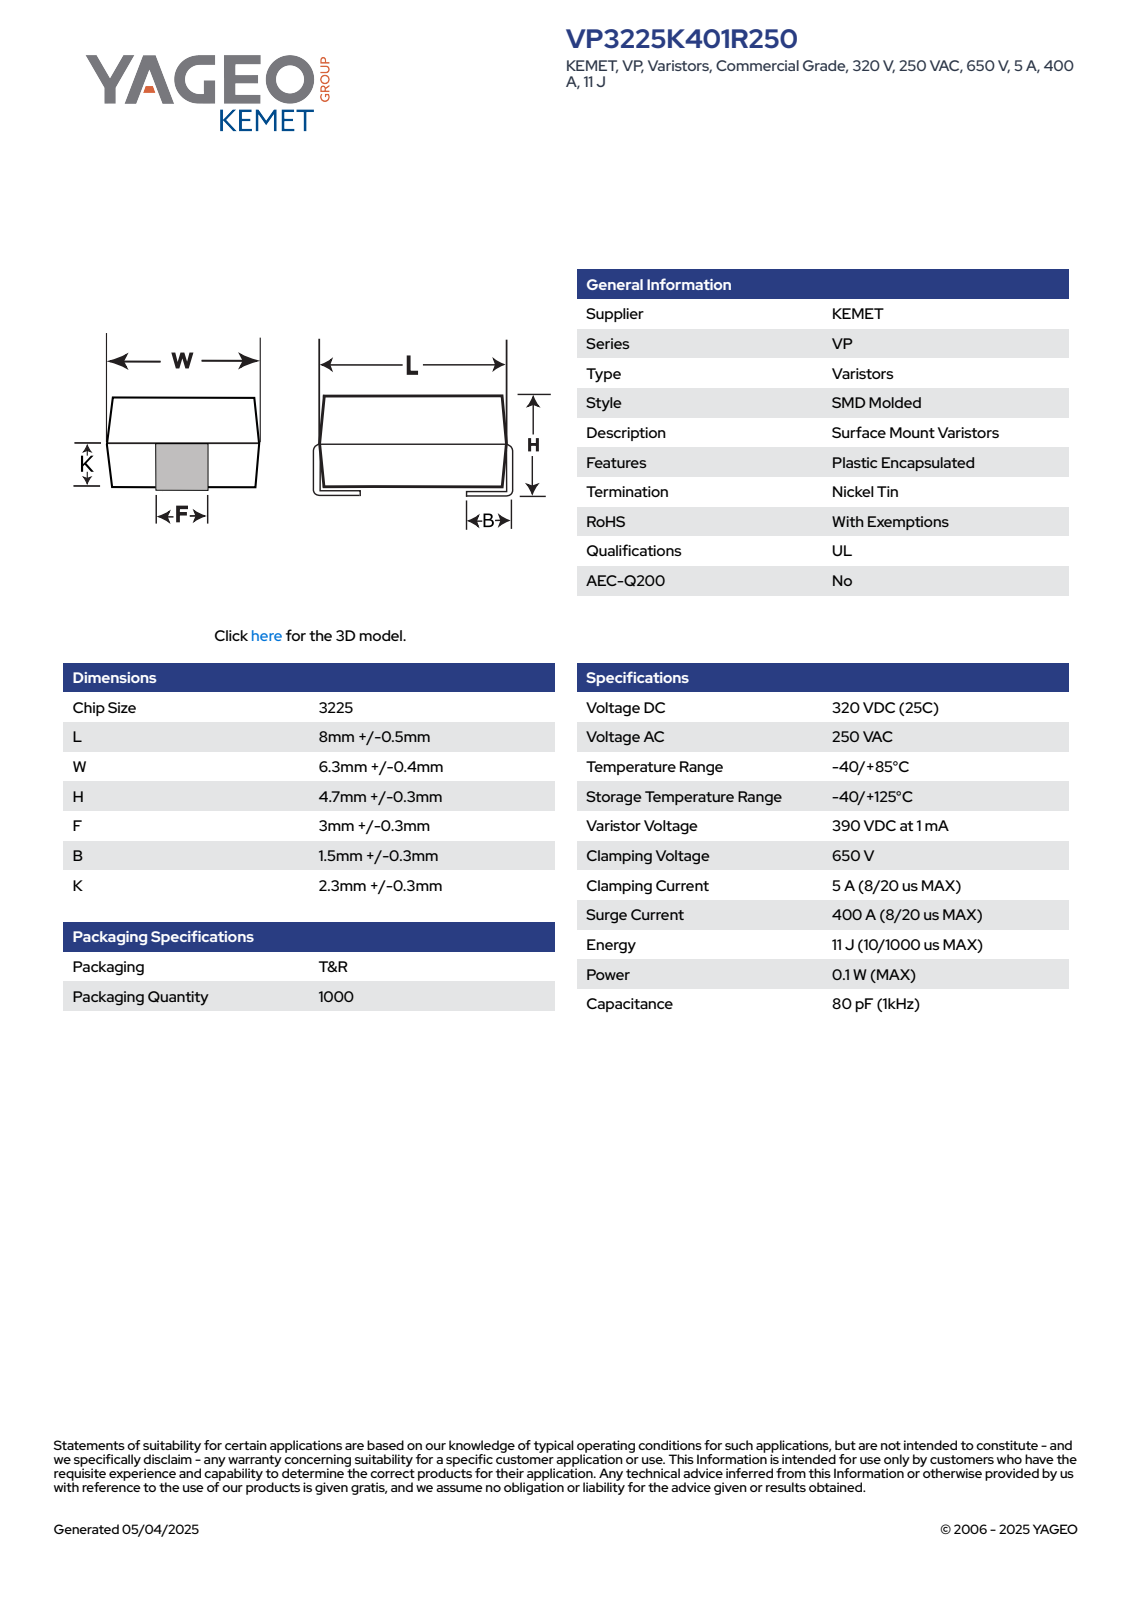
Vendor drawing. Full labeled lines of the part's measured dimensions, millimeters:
Part name (STEP PRODUCT): VS_MOLDED_3225_L8.5W6.7H5.00F3.3B1.8K2.60
STEP written by: SolidWorks 2014 (AUTOMOTIVE_DESIGN)
Units: millimetres
Bodies: 4 solids, 87 faces (83 planar, 4 cylindrical, 0 other)
Overall size (bounding box): 9.12 × 6.7 × 5
Volume: 249 mm³ · Surface area: 288 mm²
Partial cylindrical surfaces — rounded edges, fillets, slot ends (radius × count): R0.25 ×4
Main face-to-face distances: 4.7, 8.39, 8.82, 5, 8.52, 9.12, 3.3, 1.8, 1.5, 7.32
